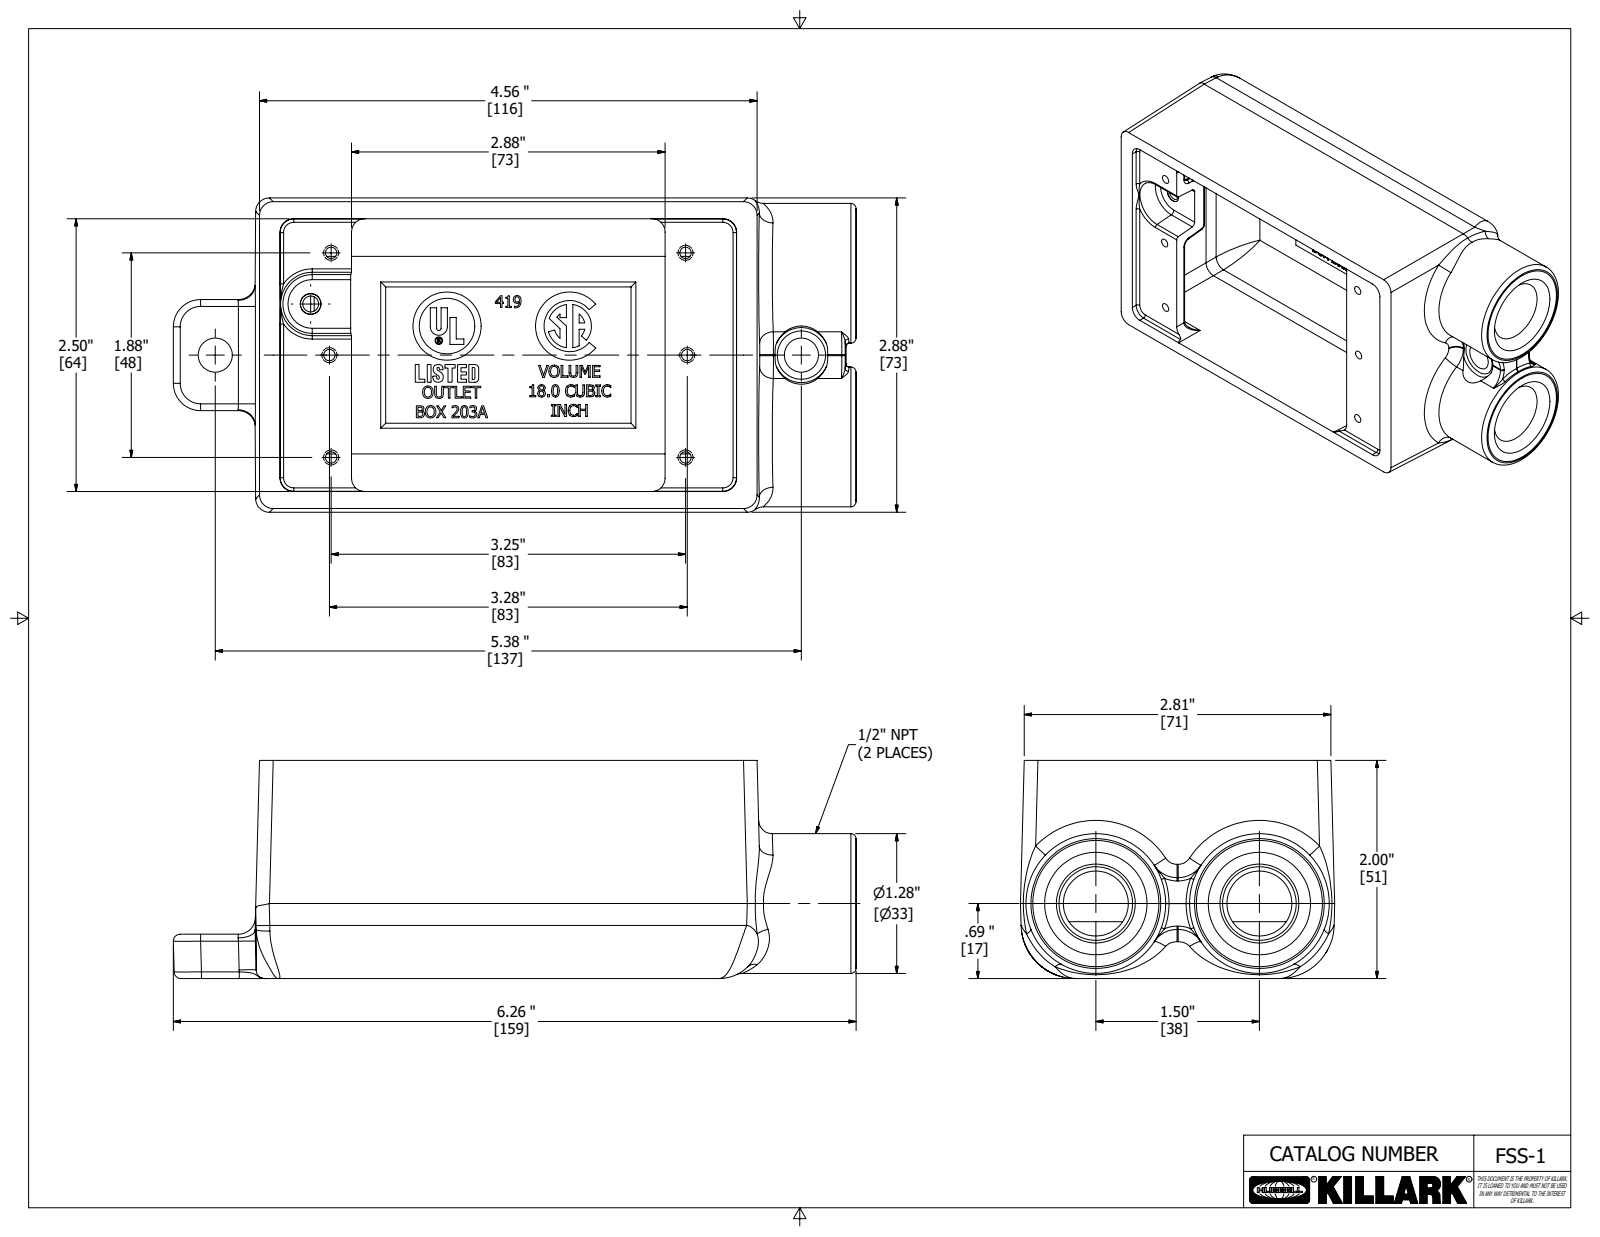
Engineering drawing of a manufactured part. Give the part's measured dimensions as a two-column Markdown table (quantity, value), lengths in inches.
| quantity | value |
| --- | --- |
| part name | 24469-2 |
| STEP written by | Autodesk Inventor 2020 (AUTOMOTIVE_DESIGN) |
| units | inches |
| bodies | 1 solid, 1137 faces (578 planar, 150 cylindrical, 409 other) |
| overall size | 6.261 × 2.881 × 2 |
| volume | 8.563 in³ |
| surface area | 95.66 in² |
| round holes (diameter × count) | 0.104 × 6, 0.595 × 2, 0.069 × 1, 0.145 × 1, 0.313 × 1, 0.625 × 1 |
| round bosses / shafts (diameter × count) | 1.281 × 2, 0.509 × 1, 0.058 × 1 |
| partial cylindrical surfaces (radius × count) | 0.125 × 32, 0.031 × 15, 0.062 × 14, 0.25 × 6, 0.375 × 4, 0.156 × 3, 0.013 × 2, 0.014 × 2 |
| main face-to-face distances | 0.156, 1.75, 2.725, 1.906, 1.594, 2, 1.844, 0.094, 0.201, 0.045 |
| hole center spacings | 0.937, 3.397, 1.417, 1.875, 3.25, 3.752, 4.413, 0.153 |
